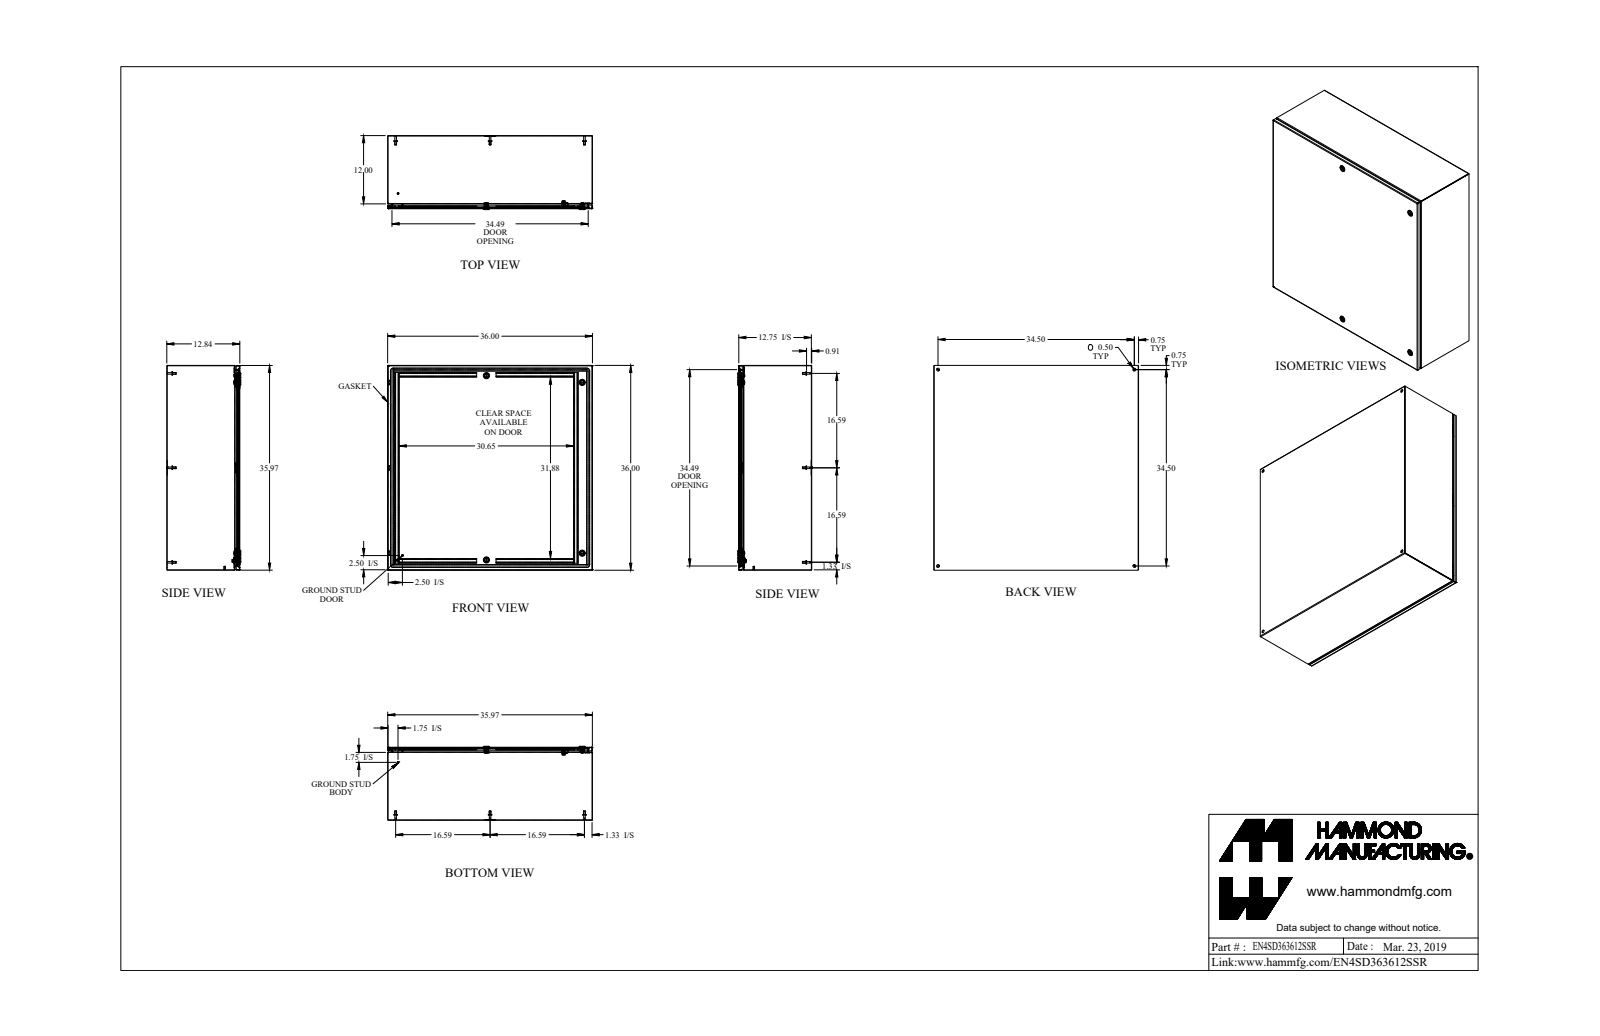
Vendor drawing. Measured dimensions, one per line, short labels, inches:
name: EN4SD363612SSR
written by: SolidWorks 2019 (AUTOMOTIVE_DESIGN)
unit: in
bodies: 57 solids, 1495 faces (769 planar, 487 cylindrical, 239 other)
size: 36 × 36 × 13.002
volume: 356 in³; area: 10 039 in²
holes: 8× ⌀0.5, 4× ⌀0.197, 4× ⌀0.387, 4× ⌀0.63, 4× ⌀0.768, 1× ⌀0.172, 1× ⌀0.196, 1× ⌀0.24, 1× ⌀0.242, 1× ⌀0.275, 1× ⌀0.375
bosses: 10× ⌀0.313, 8× ⌀0.625, 8× ⌀0.275, 5× ⌀0.625, 4× ⌀1.1, 4× ⌀0.236, 3× ⌀0.525, 2× ⌀0.785
rounds: 24× R0.01, 24× R0.048, 18× R0.036, 18× R0.108, 10× R0.062, 10× R0.094, 10× R0.25, 9× R0.016
face distances: 0.072, 12.77, 35.928, 12.698, 12.842, 35.856, 36, 0.842, 11.928, 0.038
hole spacings: 34.5, 2.488, 16.634, 16.88, 17.931, 32.267, 33.515, 35.444
